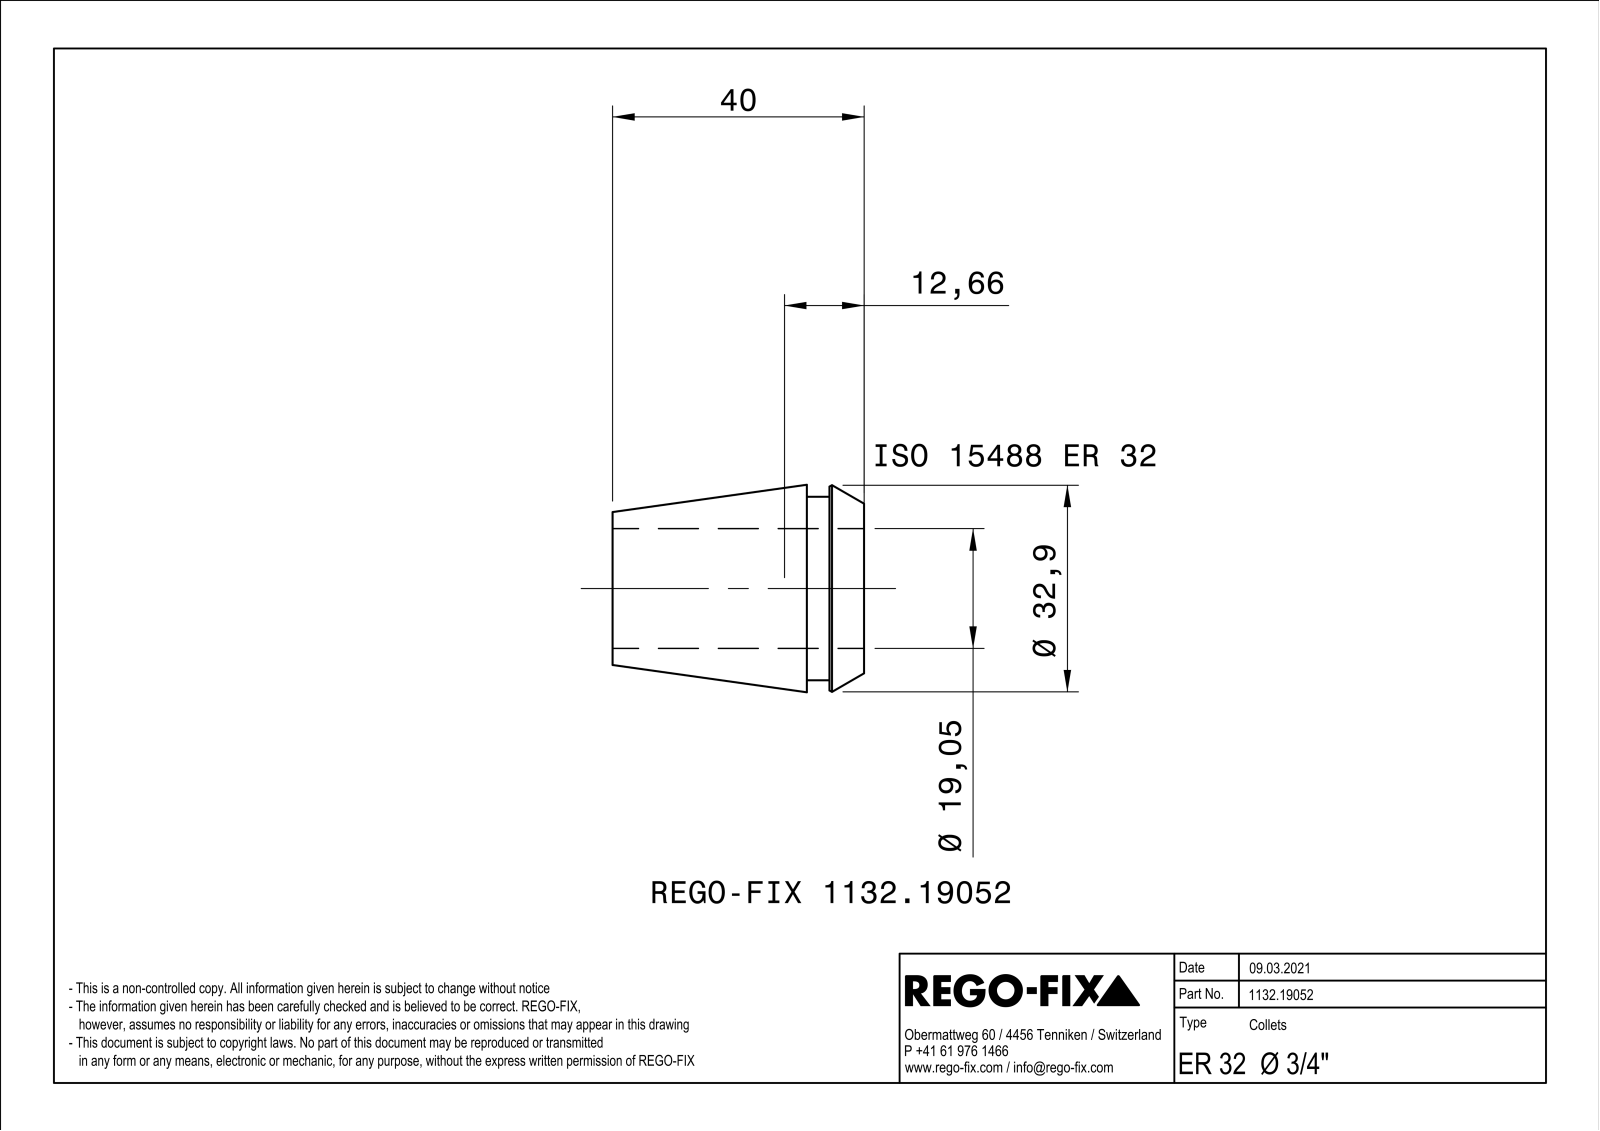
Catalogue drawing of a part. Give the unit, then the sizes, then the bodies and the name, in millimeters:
Units: millimetres
Overall size (bounding box): 40 × 32.98 × 32.98
Round holes (diameter × count): ⌀19.05 ×1
Round bosses / shafts (diameter × count): ⌀29.2 ×1
Partial cylindrical surfaces — rounded edges, fillets, slot ends (radius × count): R0.4 ×20
Main face-to-face distances: 1, 9.1, 40, 30.9, 5.5, 3.6, 34.5, 6, 0.5, 3.1
Volume: 12 210 mm³ · Surface area: 11 364 mm²
Bodies: 1 solid, 209 faces (88 planar, 41 cylindrical, 80 other)
Part name (STEP PRODUCT): NOCUT
STEP written by: SIEMENS PLM Software Solid Edge ST10 (AUTOMOTIVE_DESIGN)
